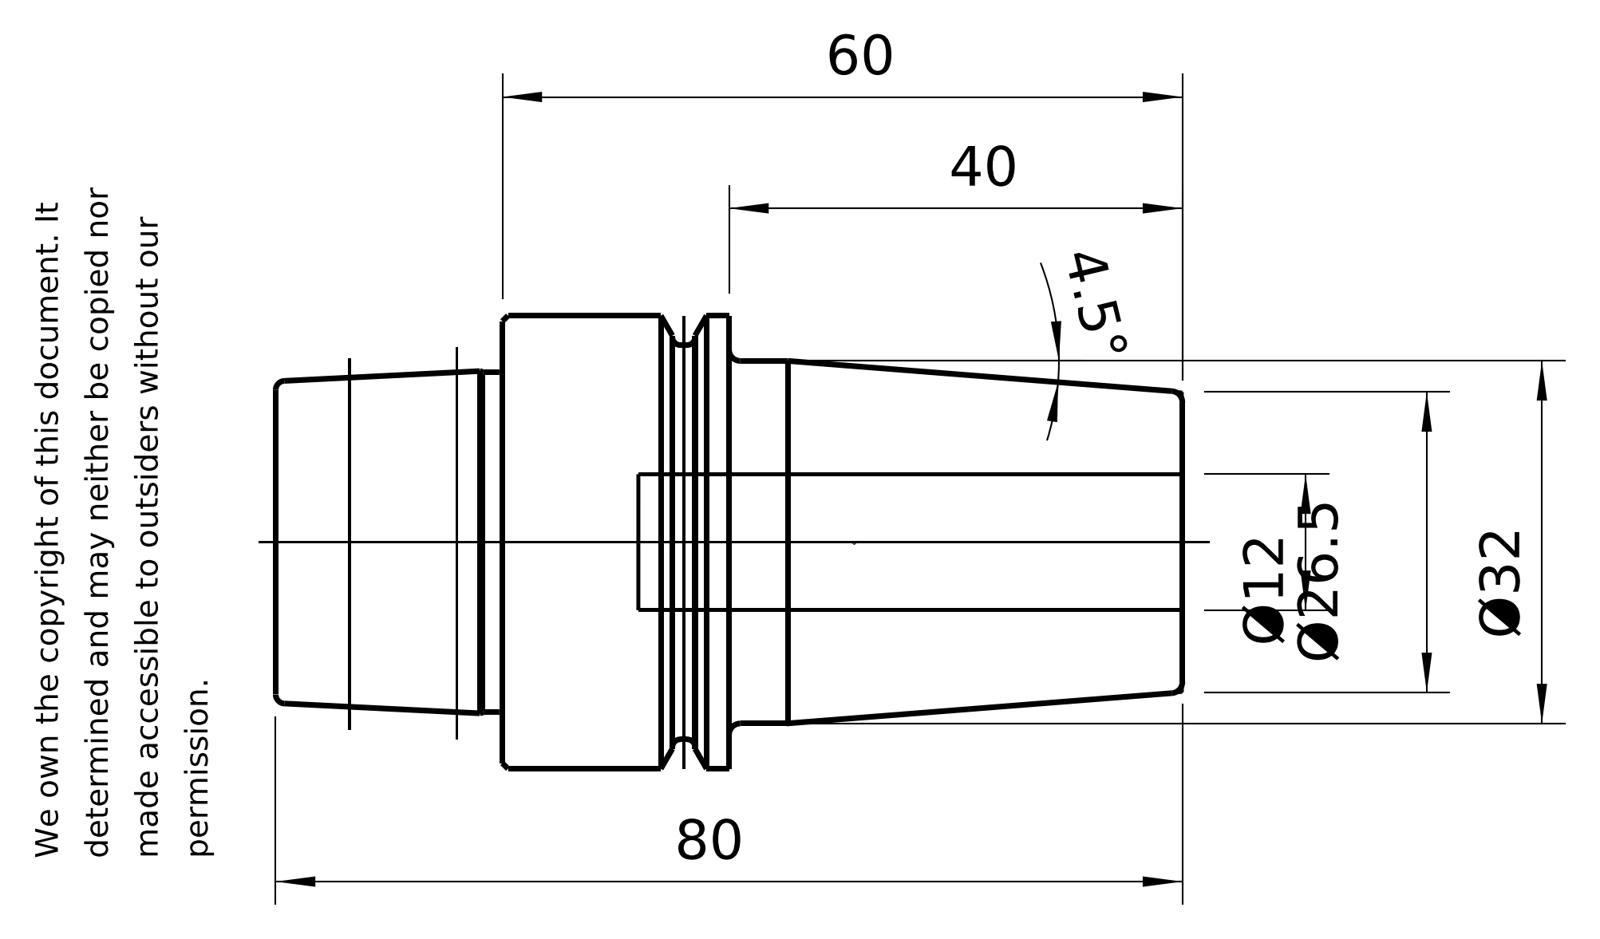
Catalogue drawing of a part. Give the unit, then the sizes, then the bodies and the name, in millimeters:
Units: millimetres
Overall size (bounding box): 79.9 × 40 × 40
Round holes (diameter × count): ⌀12 ×1, ⌀21.04 ×1, ⌀25.57 ×1
Round bosses / shafts (diameter × count): ⌀40 ×1, ⌀34.75 ×1, ⌀32 ×1, ⌀29.81 ×1
Main face-to-face distances: 7.95, 12, 60, 19.95, 40.05, 52.05, 19.9, 27.85, 39.85, 79.9
Volume: 48 534 mm³ · Surface area: 14 483 mm²
Bodies: 1 solid, 62 faces (8 planar, 18 cylindrical, 36 other)
Part name (STEP PRODUCT): E40-145-12
STEP written by: PRO/ENGINEER BY PARAMETRIC TECHNOLOGY CORPORATION, 2010430 (CONFIG_CONTROL_DESIGN)
